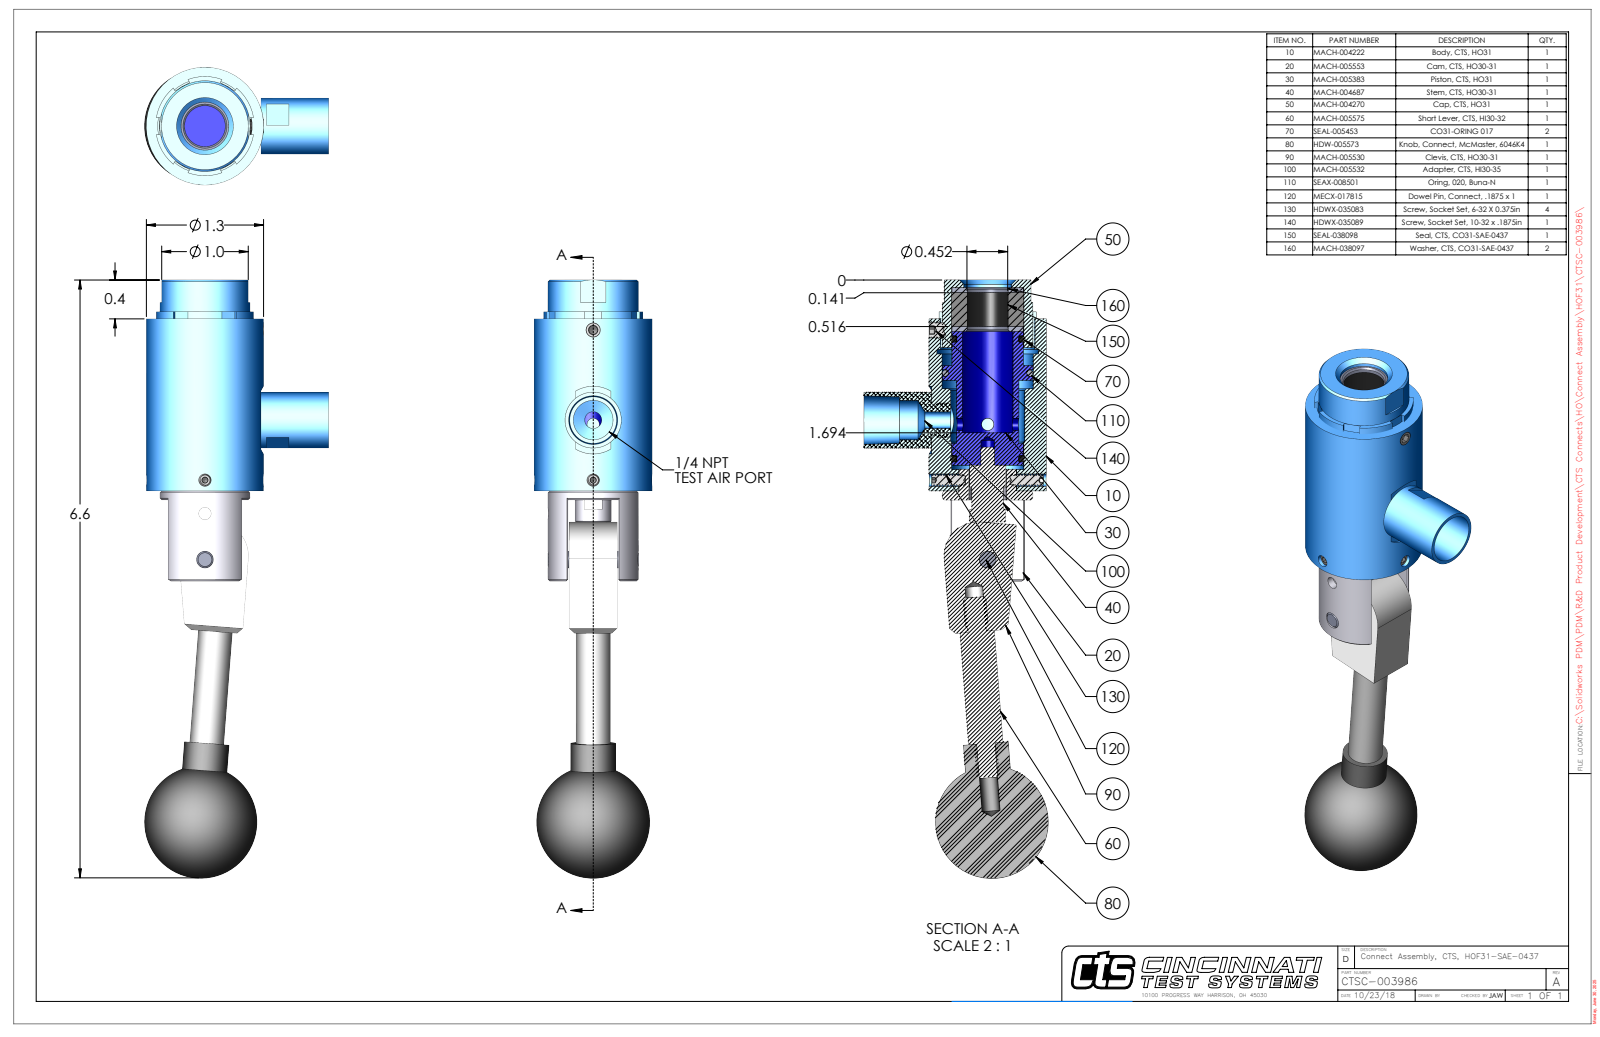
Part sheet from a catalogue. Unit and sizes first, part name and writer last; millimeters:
Units: millimetres
Overall size (bounding box): 168.4 × 51.9 × 33
Round holes (diameter × count): ⌀3.5 ×2, ⌀5.1 ×2, ⌀3.5 ×1, ⌀3.8 ×1, ⌀4 ×1, ⌀4.7 ×1, ⌀4.8 ×1, ⌀4.8 ×1, ⌀8.4 ×1, ⌀10.6 ×1, ⌀11.1 ×1, ⌀11.5 ×1
Round bosses / shafts (diameter × count): ⌀3.5 ×2, ⌀33 ×1, ⌀25.4 ×1, ⌀20.1 ×1, ⌀17.5 ×1, ⌀16 ×1, ⌀15.7 ×1, ⌀12.7 ×1
Partial cylindrical surfaces — rounded edges, fillets, slot ends (radius × count): R9.5 ×1, R9.5 ×1, R13.3 ×1, R13.9 ×1, R14.5 ×1
Main face-to-face distances: 0.3, 13.8, 1.4, 10.9, 13.5, 9.5, 14.1, 46.3, 55.8, 57.2
Hole centre spacings: 1.2, 13, 25.1, 25.3, 26.5, 38
Volume: 73 950 mm³ · Surface area: 29 550 mm²
Bodies: 14 solids, 533 faces (173 planar, 218 cylindrical, 142 other)
Part name (STEP PRODUCT): CTSC-003986
STEP written by: SolidWorks 2023 (AUTOMOTIVE_DESIGN)
